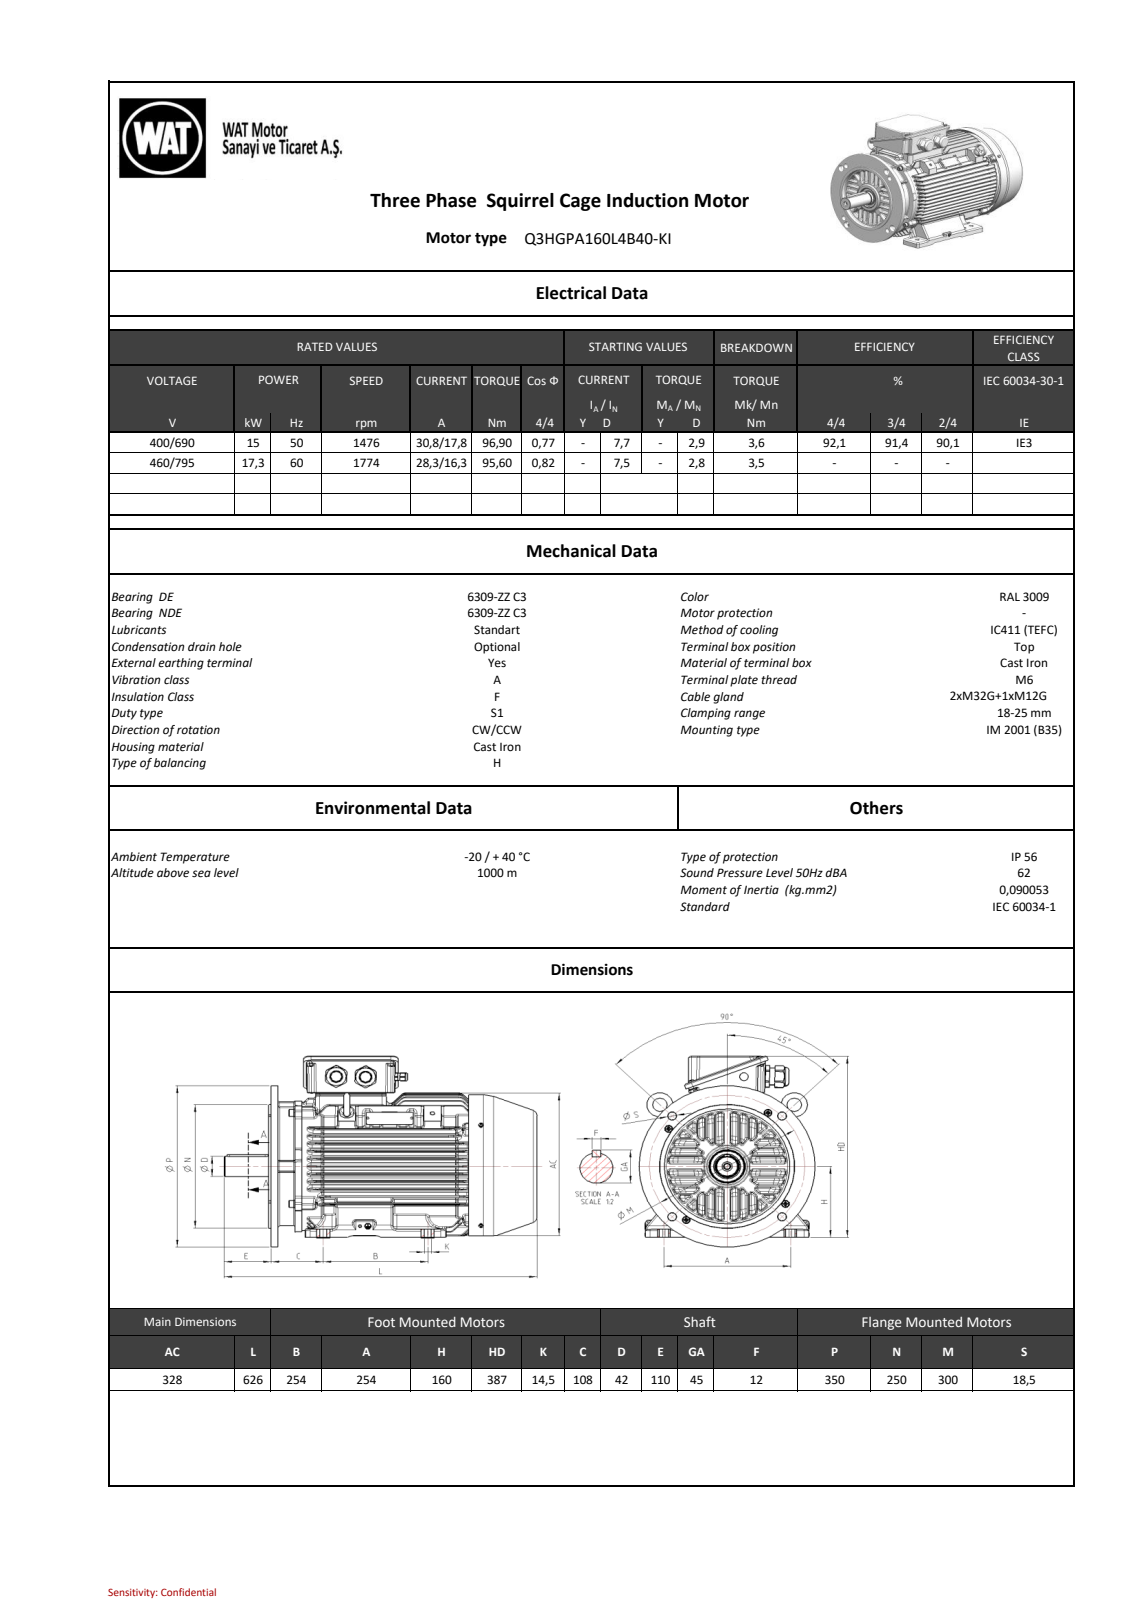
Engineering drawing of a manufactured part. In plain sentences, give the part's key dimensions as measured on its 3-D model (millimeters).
The part is named "26001C7CEAC1xhp1". Its 3-D file was written by "SIEMENS PLM Software NX 11.0 (AUTOMOTIVE_DESIGN)". It is 0 solids with 6512 faces: 1177 planar, 1837 cylindrical and 3498 other. Overall it measures 625.5 by 402.41 by 350 millimeters. Round holes: 8 of diameter 5.5, 7 of diameter 9, 6 of diameter 4.2, 4 of diameter 5.3, 4 of diameter 11, 4 of diameter 18.5, 4 of diameter 23, 2 of diameter 2.5, 2 of diameter 10.9, 2 of diameter 19, 2 of diameter 21, 1 of diameter 5.2. Round bosses or shafts: 4 of diameter 16, 2 of diameter 34.5, 2 of diameter 31.25, 2 of diameter 30, 1 of diameter 350, 1 of diameter 317, 1 of diameter 282, 1 of diameter 256. Partial cylindrical surfaces (rounded edges, fillets, slot ends): 213 of radius 5, 181 of radius 3, 146 of radius 4, 120 of radius 1.5, 82 of radius 2, 58 of radius 1.8, 45 of radius 3.5, 28 of radius 6. The main face-to-face distances are 137.45, 15.17, 30.42, 15.25, 122.2, 45.73, 106.89, 30.56, 15.31, 107.03. The hole center spacings are 136, 26.31, 144, 189.04, 225.26, 292.89, 203.65, 0.77.
